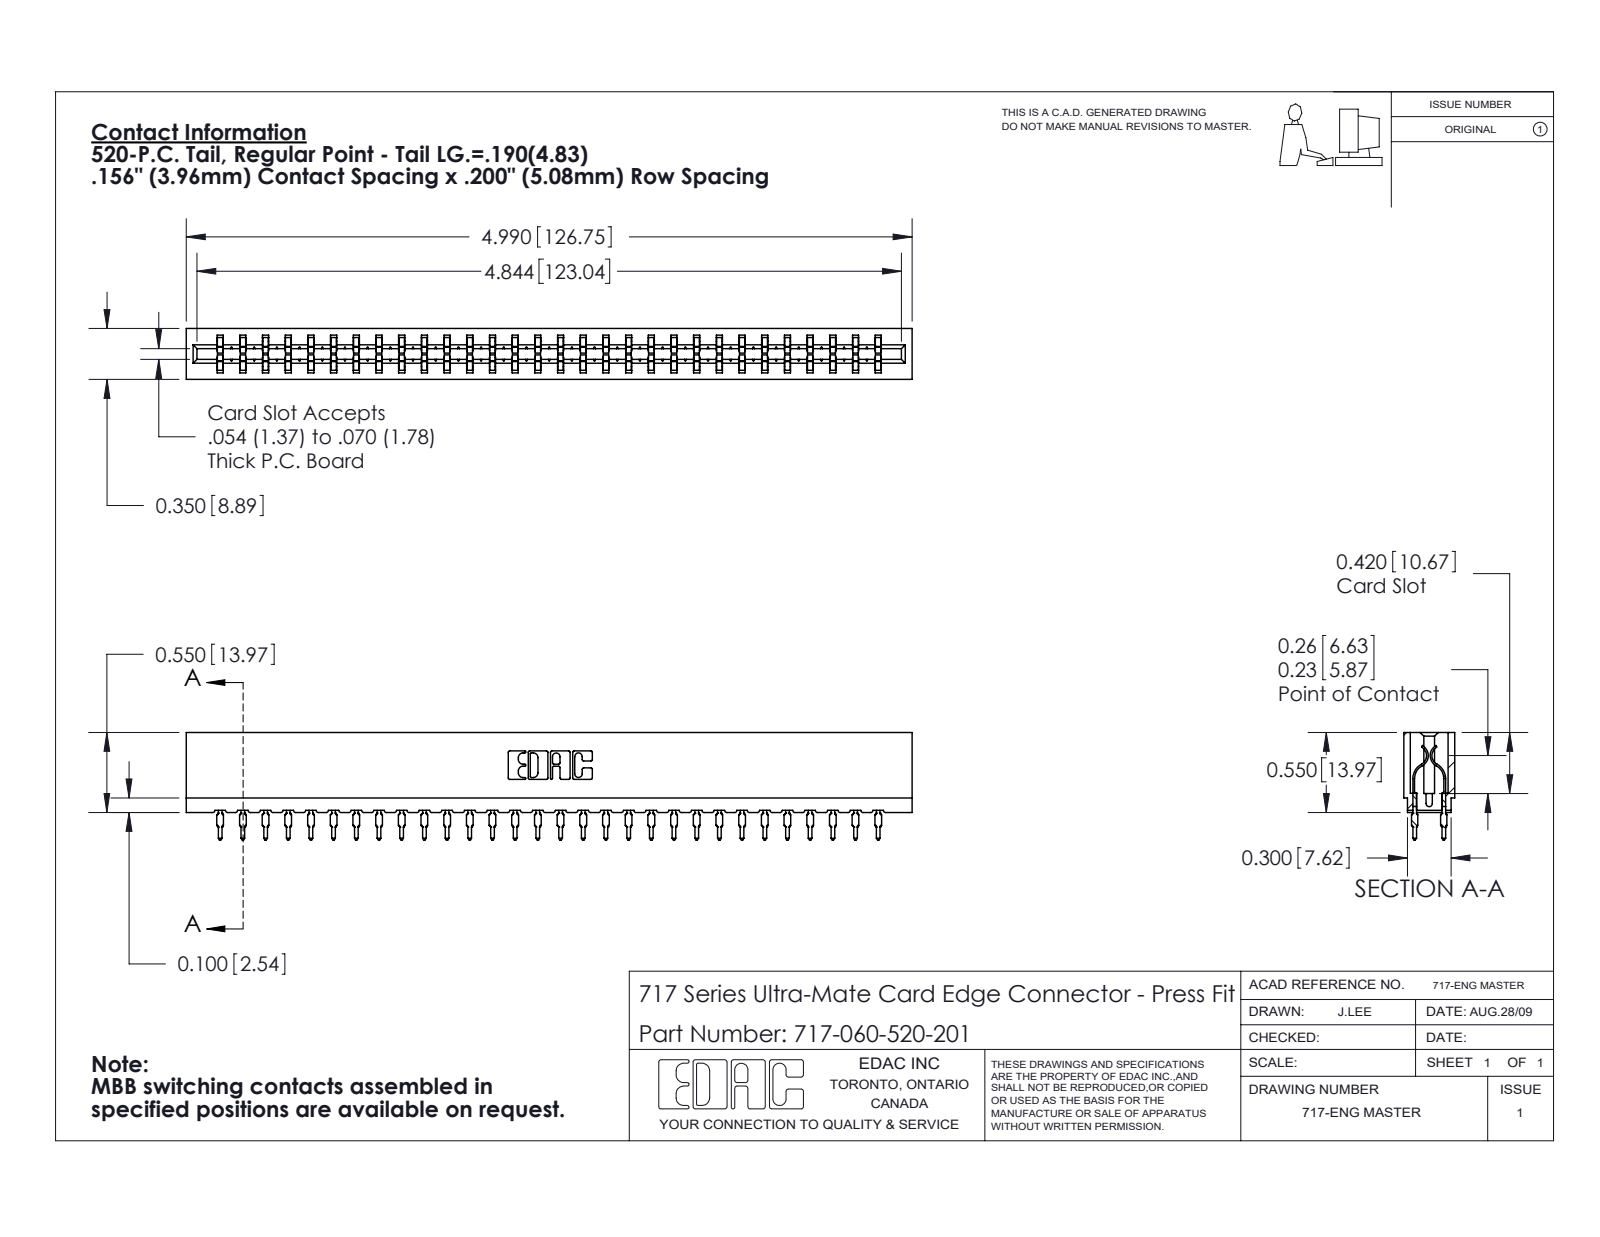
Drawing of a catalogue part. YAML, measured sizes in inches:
part_name: "717-060-520-201; 717 Part_Insulator Option - 06; 745-292-001_520"
step_written_by: "SolidWorks 2020 (CONFIG_CONTROL_DESIGN)"
units: inches
bodies: {solids: 61, faces: 5494, planar: 2844, cylindrical: 1090, other: 1560}
overall_size: [4.99, 0.739, 0.35]
volume: 0.67
surface_area: 25.32
partial_cylinders:
  - {radius: 0.021, count: 120}
  - {radius: 0.015, count: 60}
  - {radius: 0.01, count: 22}
  - {radius: 0.005, count: 8}
  - {radius: 0.011, count: 8}
  - {radius: 0.007, count: 6}
  - {radius: 0.031, count: 6}
  - {radius: 0.026, count: 3}
face_to_face_distances: [0.212, 0.138, 0.35, 0.063, 0.287, 0.076, 0.149, 0.074, 0.156, 0.045]
